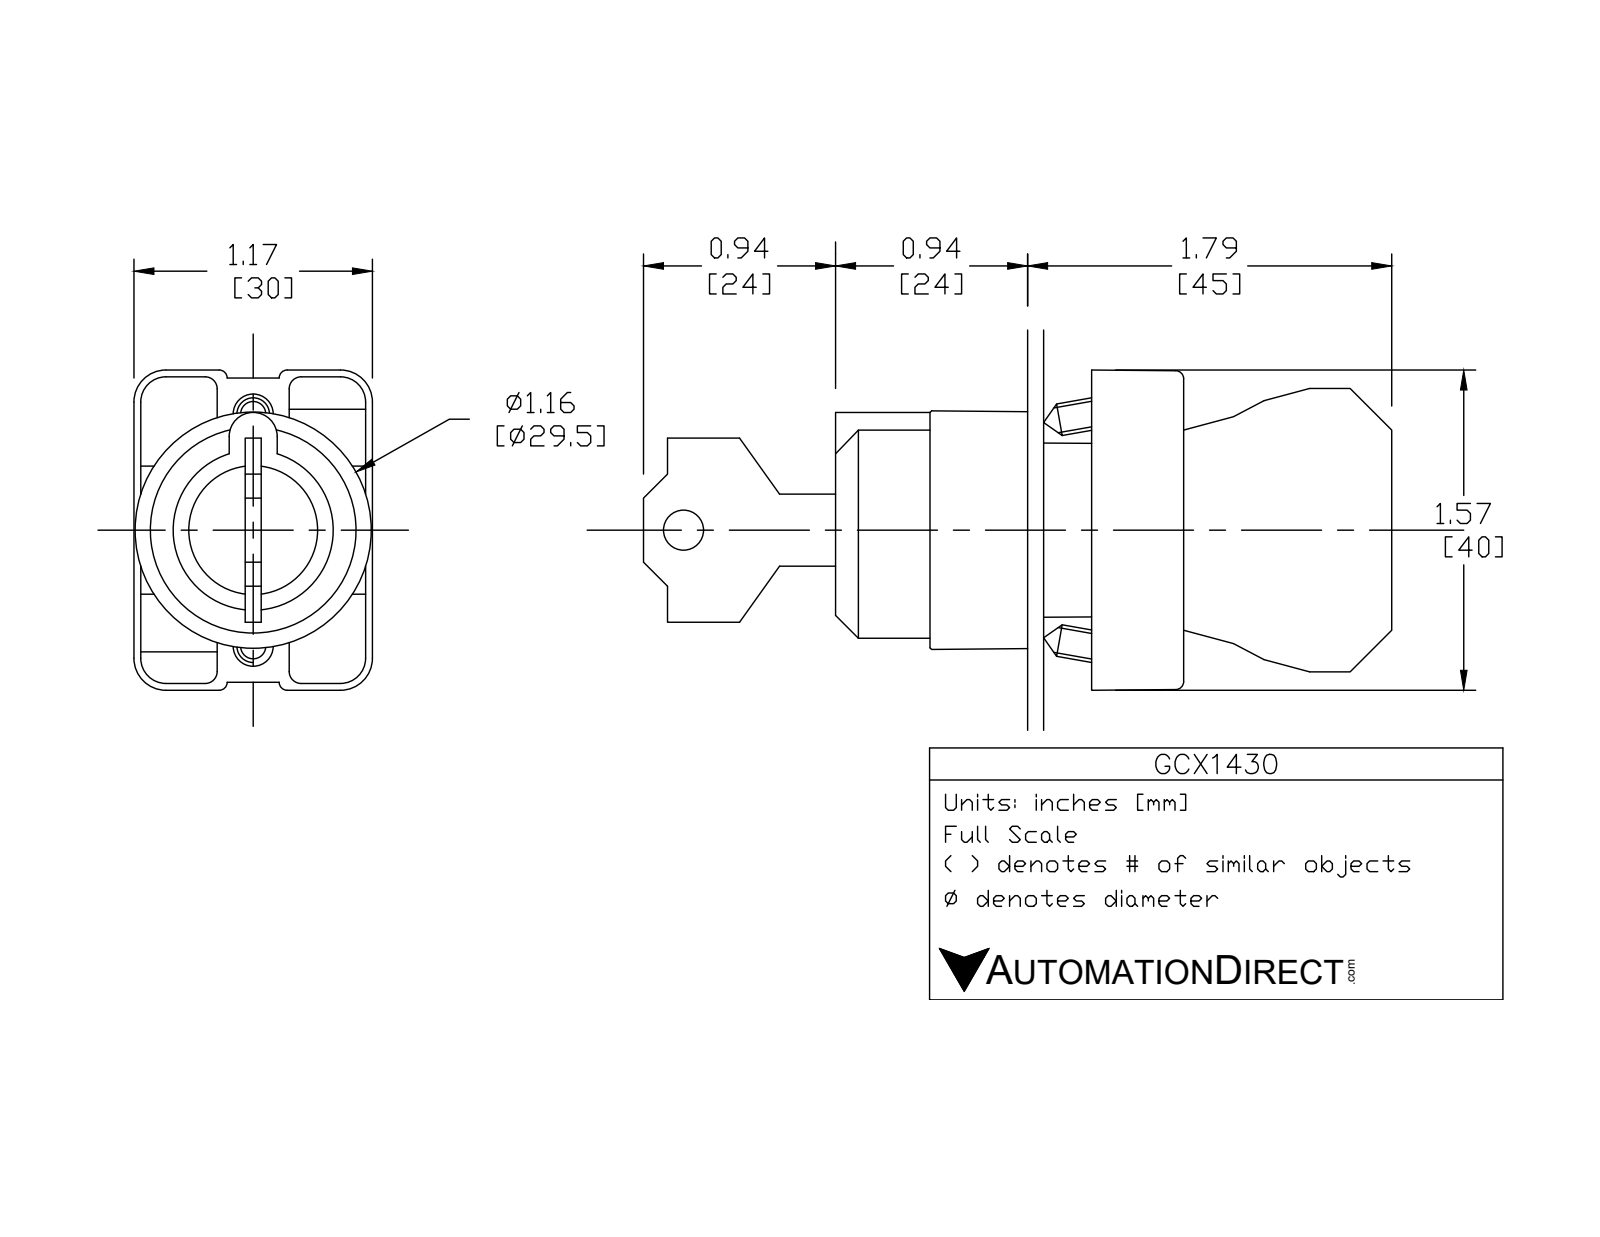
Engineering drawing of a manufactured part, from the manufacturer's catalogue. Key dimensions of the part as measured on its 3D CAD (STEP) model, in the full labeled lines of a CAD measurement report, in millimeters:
Part name (STEP PRODUCT): GCX1430 OPERATOR; ecx1029; GCX1430; ecx1040
STEP written by: SolidWorks 2016 (AUTOMOTIVE_DESIGN)
Units: millimetres
Bodies: 7 solids, 405 faces (235 planar, 142 cylindrical, 28 other)
Overall size (bounding box): 67.3 × 40.2 × 29.9
Volume: 32 890 mm³ · Surface area: 20 830 mm²
Round holes (diameter × count): ⌀2 ×2, ⌀3.1 ×2, ⌀3.3 ×2, ⌀2.2 ×1, ⌀5 ×1, ⌀15 ×1, ⌀22.3 ×1, ⌀22.6 ×1, ⌀26 ×1
Round bosses / shafts (diameter × count): ⌀4 ×2, ⌀29.8 ×1, ⌀25.5 ×1, ⌀24.5 ×1, ⌀24 ×1, ⌀21.7 ×1, ⌀19.8 ×1, ⌀14.5 ×1
Partial cylindrical surfaces — rounded edges, fillets, slot ends (radius × count): R1.5 ×24, R1 ×12, R3.1 ×12, R4 ×12, R1 ×6, R3.3 ×2, R0.5 ×1, R1.6 ×1
Main face-to-face distances: 18.3, 14.7, 0.8, 0.8, 17.5, 15.2, 13.7, 16.2, 14.7, 3.1
Hole centre spacings: 6, 13.8, 12, 12.4
